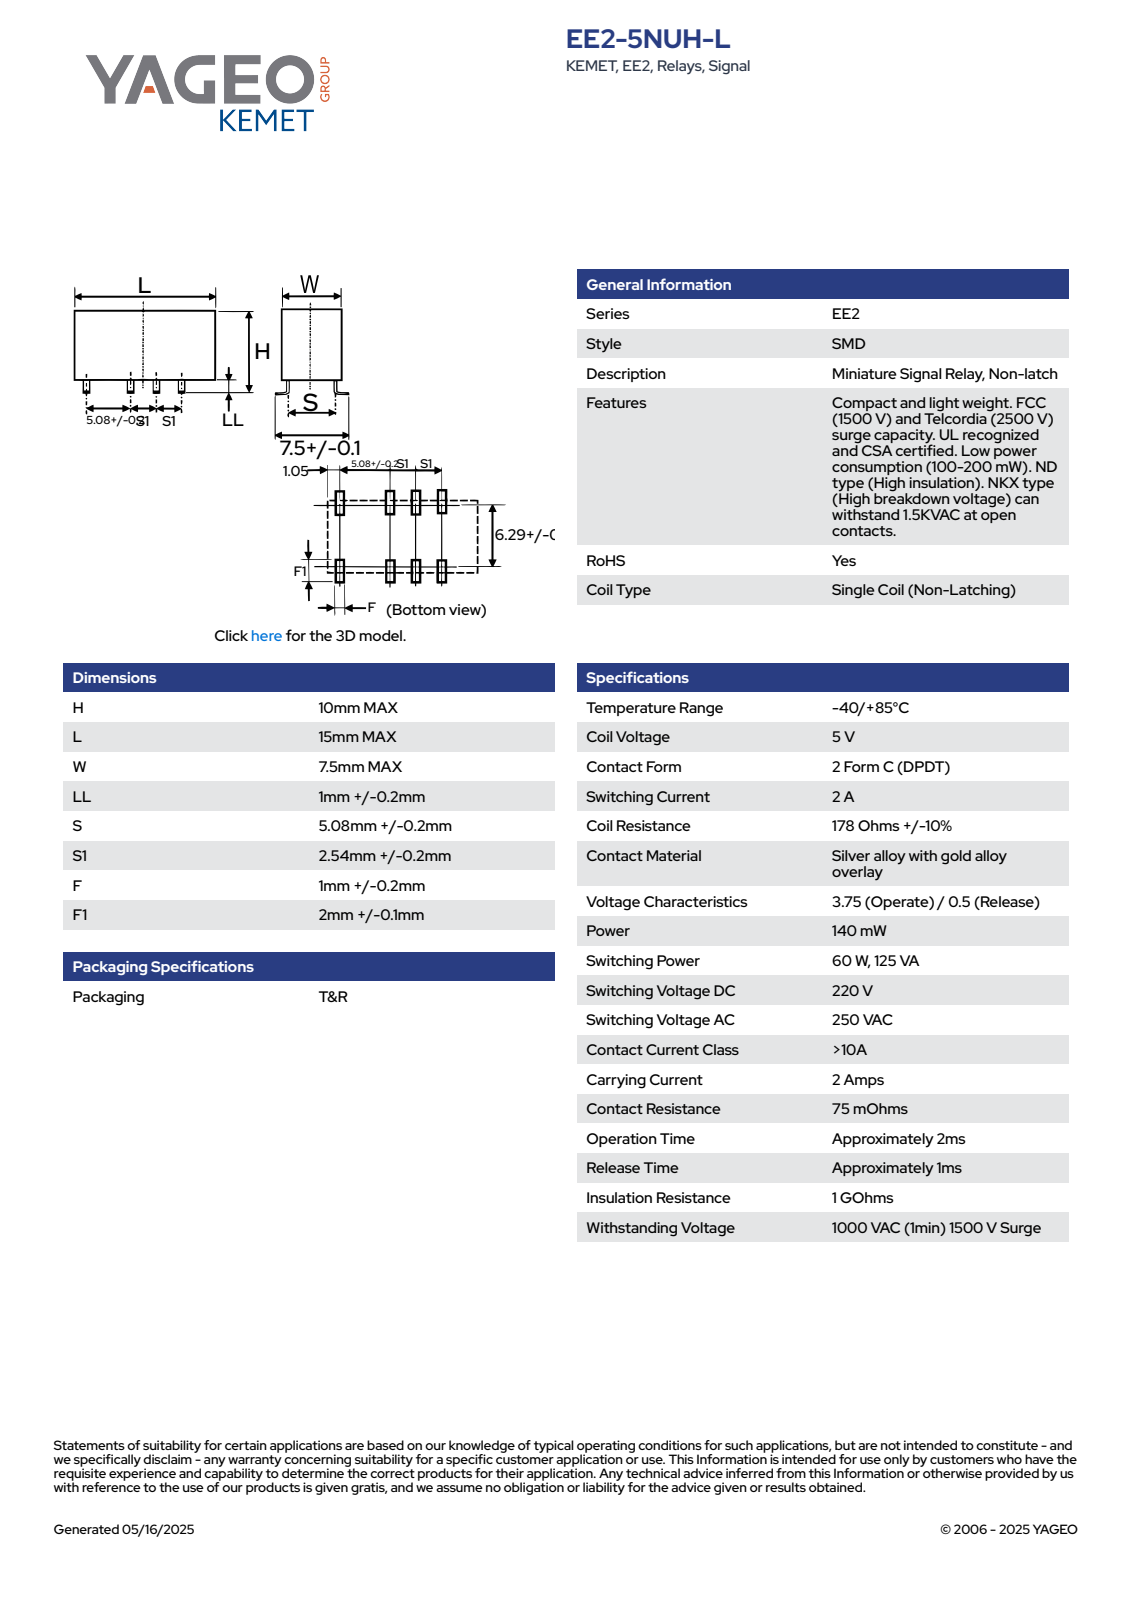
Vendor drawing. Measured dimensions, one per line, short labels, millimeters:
name: IR_TEE2MFS_L15W7.5H10
written by: SolidWorks 2014 (AUTOMOTIVE_DESIGN)
unit: mm
bodies: 1 solid, 116 faces (116 planar, 0 cylindrical, 0 other)
size: 15 × 10.01 × 7.5
volume: 992 mm³; area: 649 mm²
face distances: 7.5, 8.8, 15, 1.2, 10, 1.33, 6.17, 0.5, 5.08, 2.54
